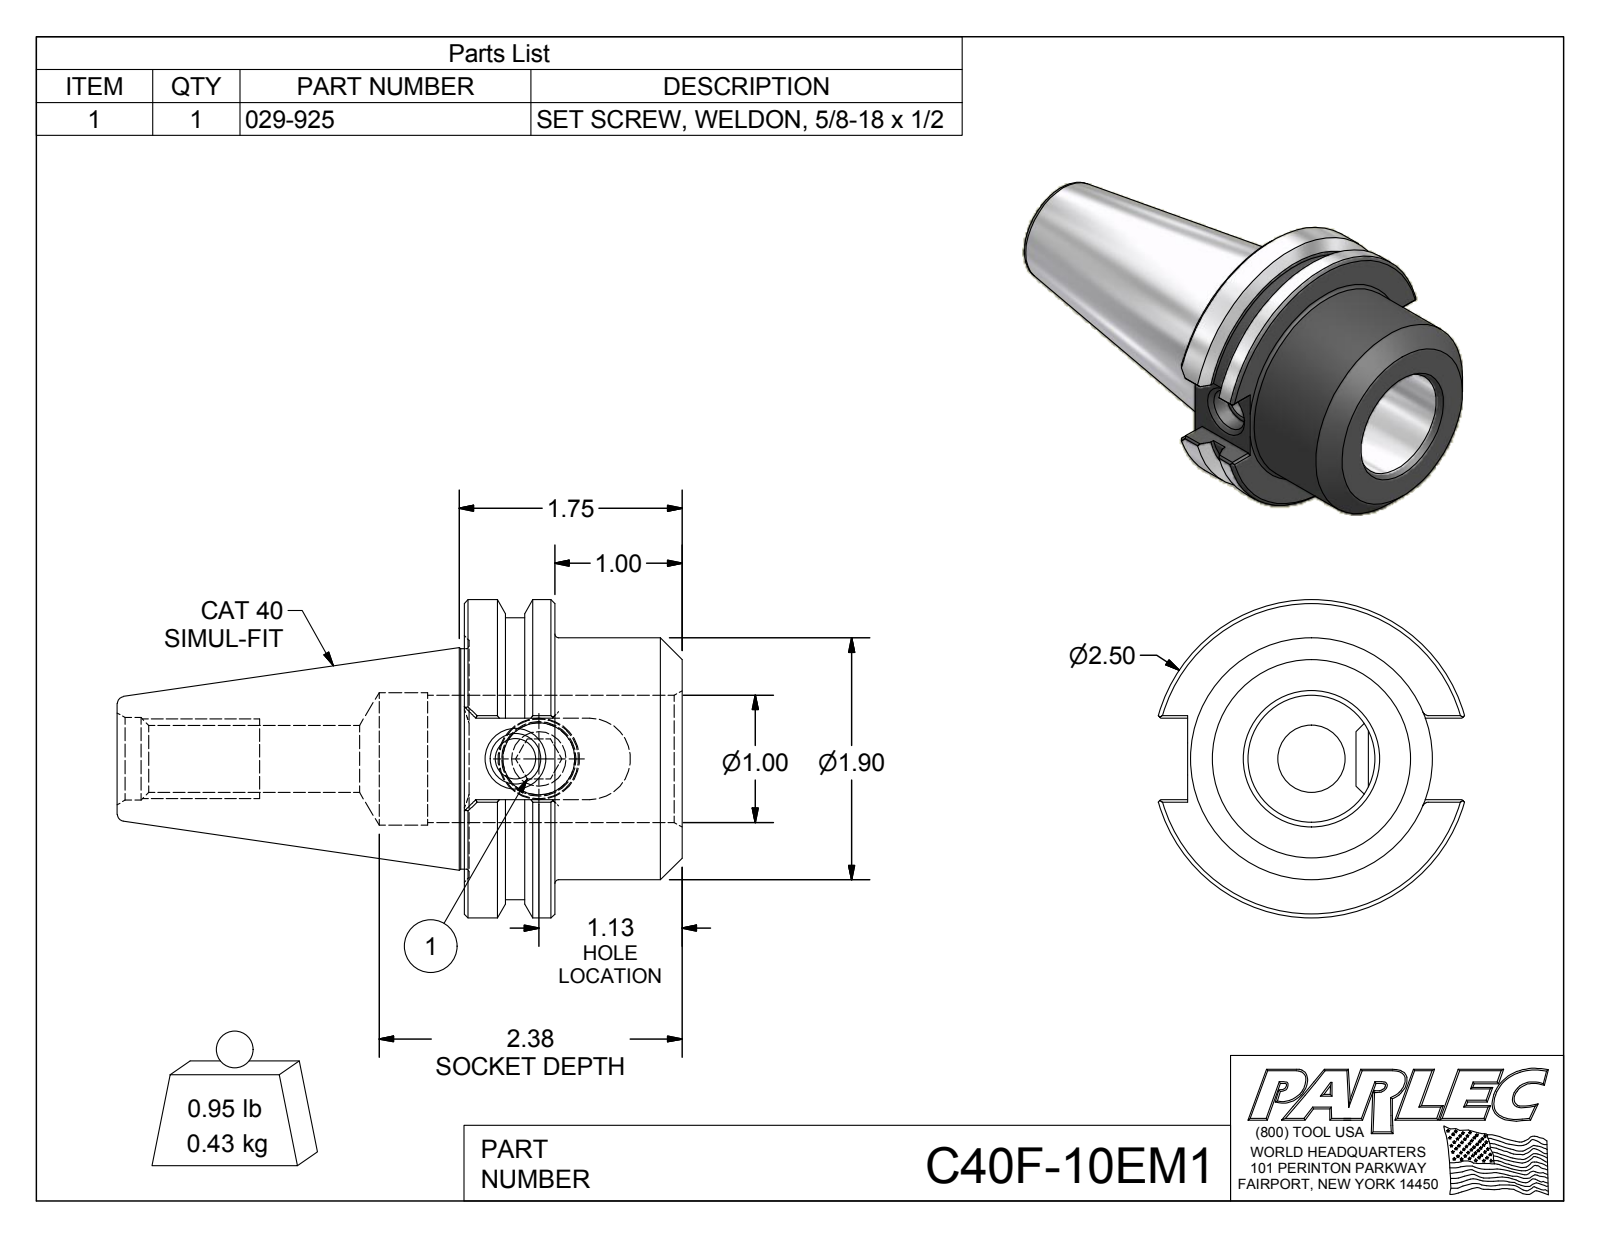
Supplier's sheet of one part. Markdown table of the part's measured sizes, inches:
| quantity | value |
| --- | --- |
| part name | C40F-10EM1; C40F-10EM1-1; 029-925 |
| STEP written by | Autodesk Inventor 2012 (AUTOMOTIVE_DESIGN) |
| units | inches |
| bodies | 2 solids, 87 faces (43 planar, 17 cylindrical, 27 other) |
| overall size | 4.438 × 2.5 × 2.406 |
| volume | 7.394 in³ |
| surface area | 44.48 in² |
| round holes (diameter × count) | 0.315 × 1, 0.399 × 1, 0.527 × 1, 0.565 × 1, 0.648 × 1, 1 × 1, 1.04 × 1 |
| round bosses / shafts (diameter × count) | 2.5 × 1, 2.215 × 1, 1.9 × 1, 1.73 × 1, 0.625 × 1 |
| partial cylindrical surfaces (radius × count) | 0.32 × 1 |
| main face-to-face distances | 0.711, 1, 1.711, 0.037, 1.86, 0.64, 0.673, 1.673, 0.315, 2.727 |
| hole center spacings | 0.185 |
